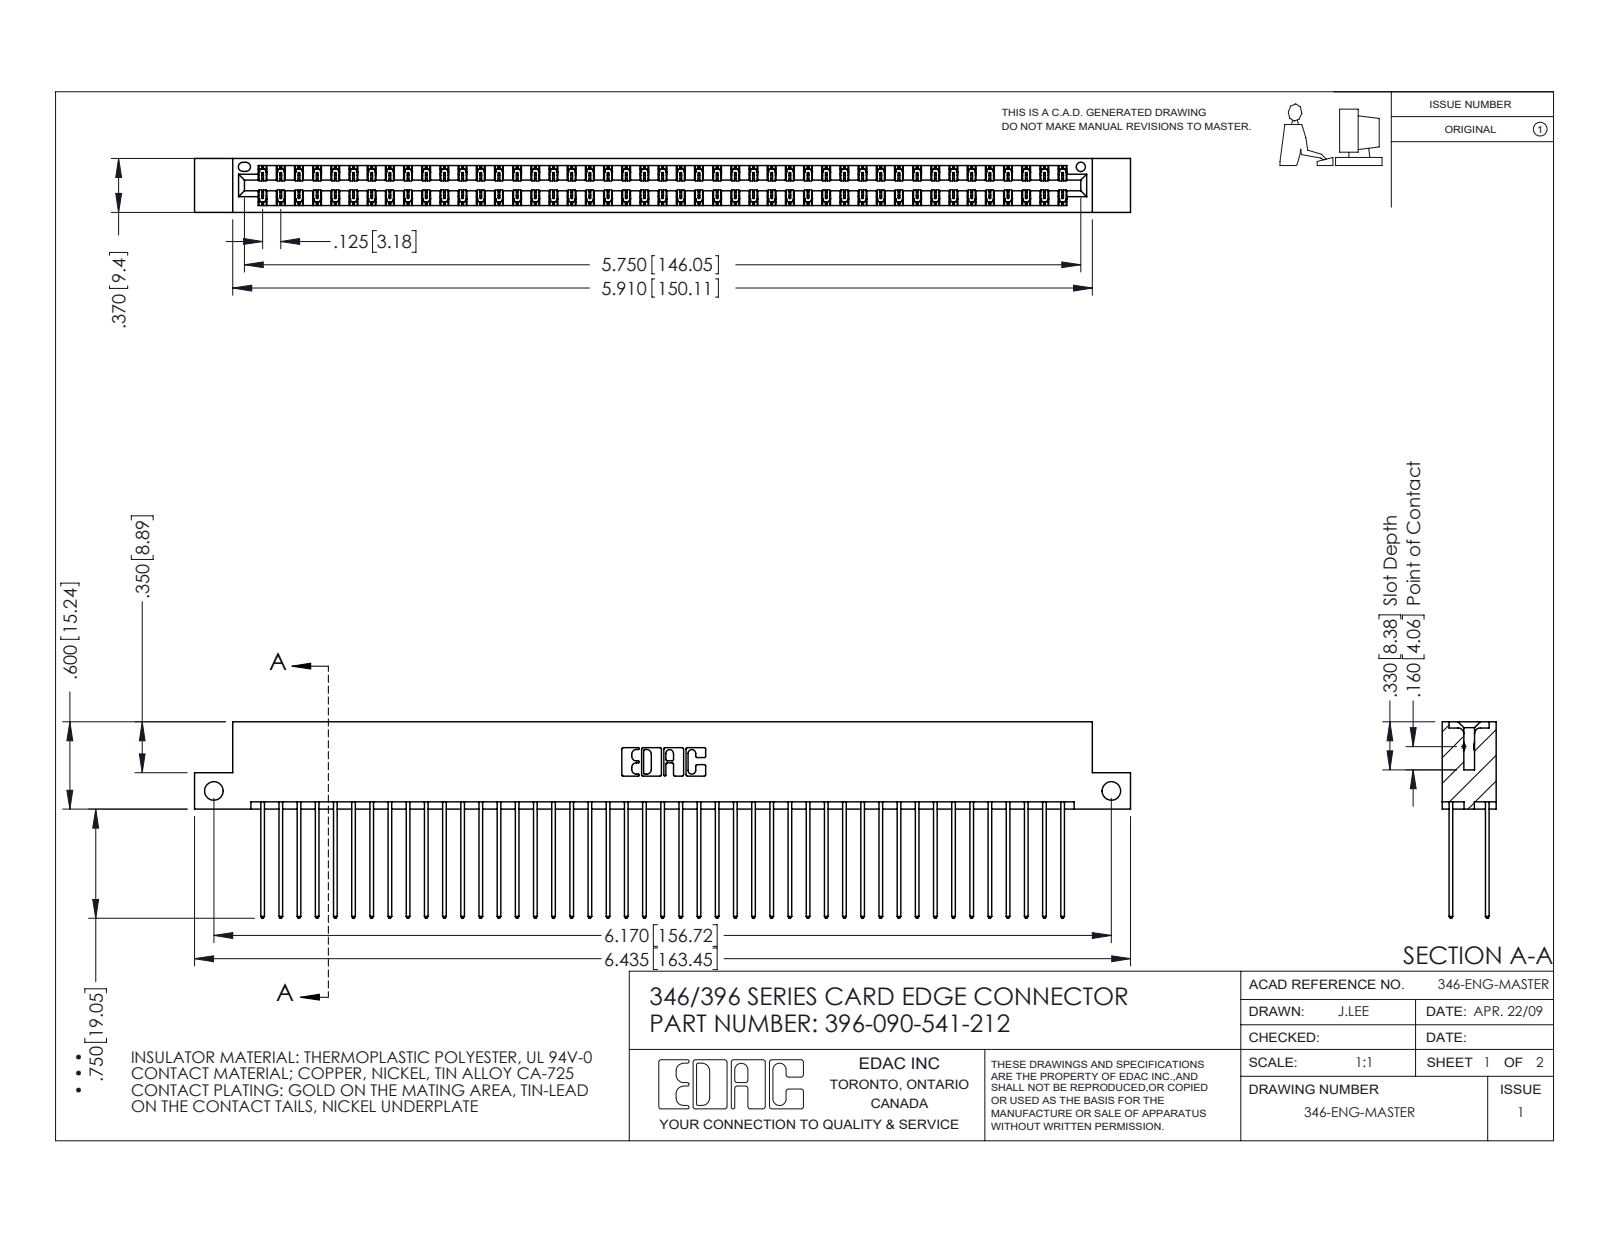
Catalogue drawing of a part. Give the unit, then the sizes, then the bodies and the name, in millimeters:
Units: millimetres
Overall size (bounding box): 163.4 × 34.3 × 9.4
Round holes (diameter × count): ⌀3.3 ×2, ⌀1.6 ×1
Partial cylindrical surfaces — rounded edges, fillets, slot ends (radius × count): R0.2 ×135, R0.3 ×90, R0.3 ×22, R0.2 ×6, R0.8 ×6, R0.7 ×3, R0.4 ×2, R0.6 ×2
Main face-to-face distances: 1.2, 8.2, 6.4, 1.8, 7.6, 0.6, 9.4, 7, 5.7, 3.8
Hole centre spacings: 156.7
Volume: 16 390 mm³ · Surface area: 24 920 mm²
Bodies: 91 solids, 4802 faces (3226 planar, 1576 cylindrical, 0 other)
Part name (STEP PRODUCT): 346 Part_Flush Mounting Lugs - Side Mount; 345-292-001_345-293-141; 396-090-541-212
STEP written by: SolidWorks 2016 (CONFIG_CONTROL_DESIGN)
